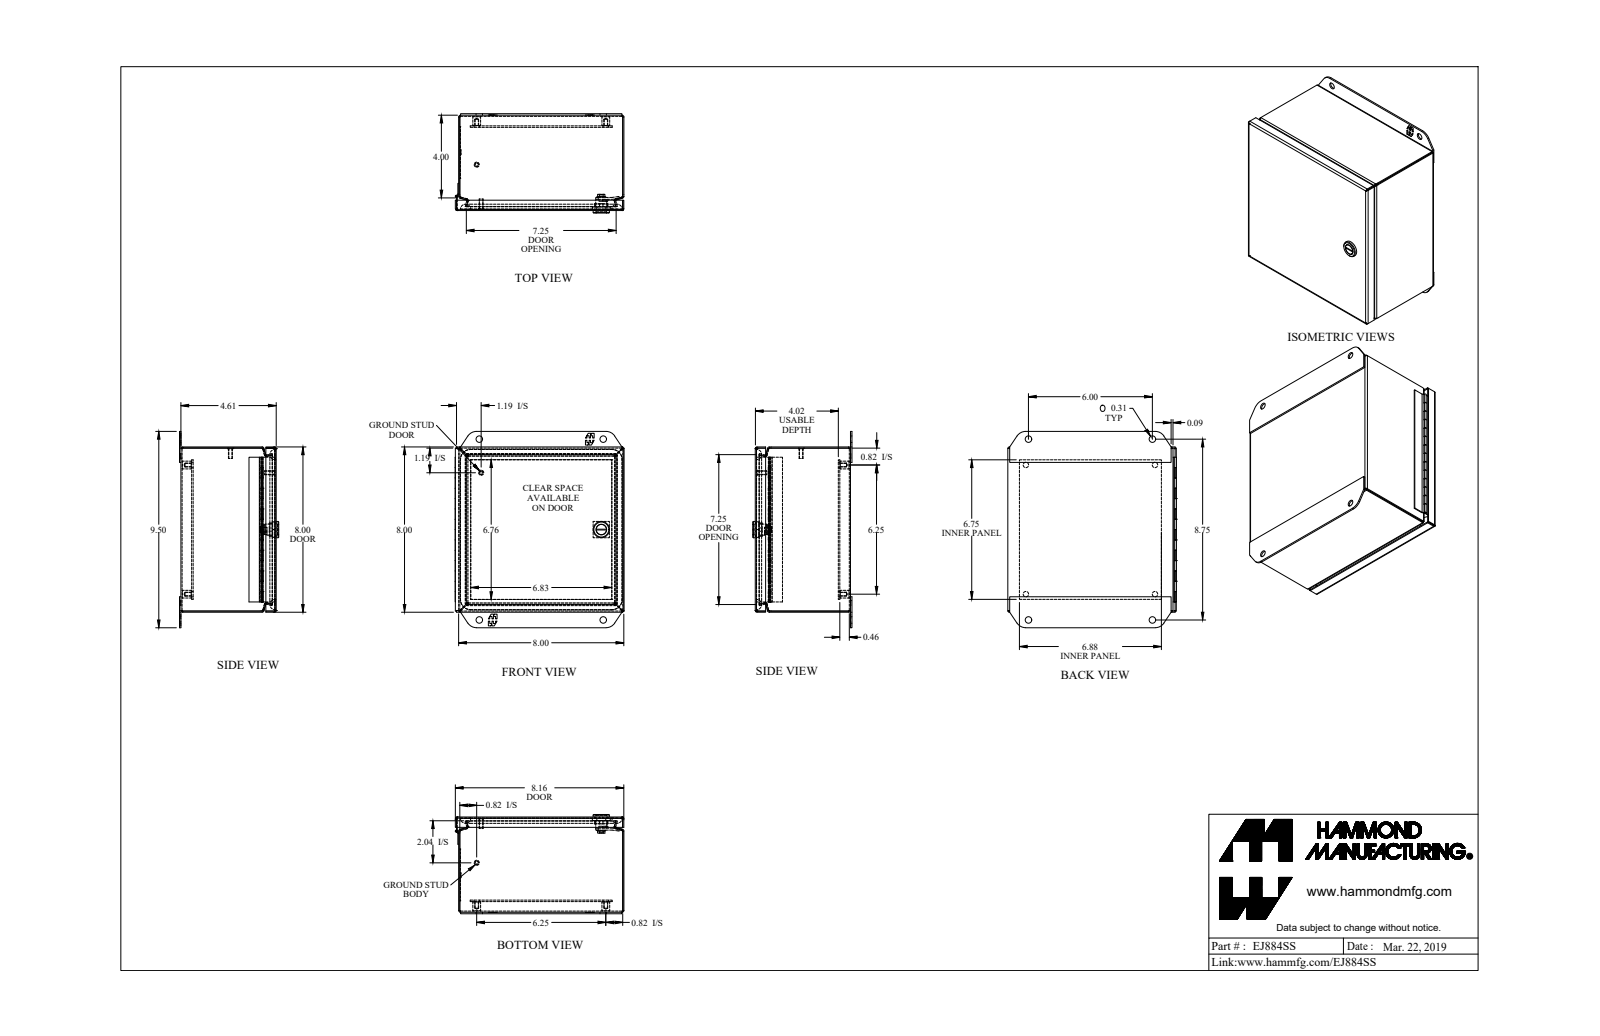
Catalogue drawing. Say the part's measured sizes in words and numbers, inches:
The part is named "EJ884SS_Default". Its 3-D file was written by "SolidWorks 2019 (CONFIG_CONTROL_DESIGN)". It is 16 solids with 656 faces: 370 planar, 190 cylindrical and 96 other. Overall it measures 9.5 by 8.165 by 4.805 inches. Its volume is 24.9 cubic inches and its surface area 817.7 square inches. Round holes: 4 of diameter 0.156, 4 of diameter 0.265, 4 of diameter 0.313, 1 of diameter 0.05, 1 of diameter 0.516. Round bosses or shafts: 4 of diameter 0.375, 2 of diameter 0.25, 2 of diameter 0.19, 1 of diameter 0.788, 1 of diameter 0.535, 1 of diameter 0.496, 1 of diameter 0.435, 1 of diameter 0.1. Partial cylindrical surfaces (rounded edges, fillets, slot ends): 16 of radius 0.029, 16 of radius 0.086, 12 of radius 0.281, 4 of radius 0.25, 4 of radius 0.499, 4 of radius 0.5, 2 of radius 0.06, 1 of radius 0.03. The main face-to-face distances are 0.057, 4.554, 7.943, 0.072, 0.589, 7.886, 8, 4.611, 4.497, 4.094. The hole center spacings are 6.25, 1.256, 7.502, 3.133, 6.252, 9.684, 4.376, 6.
